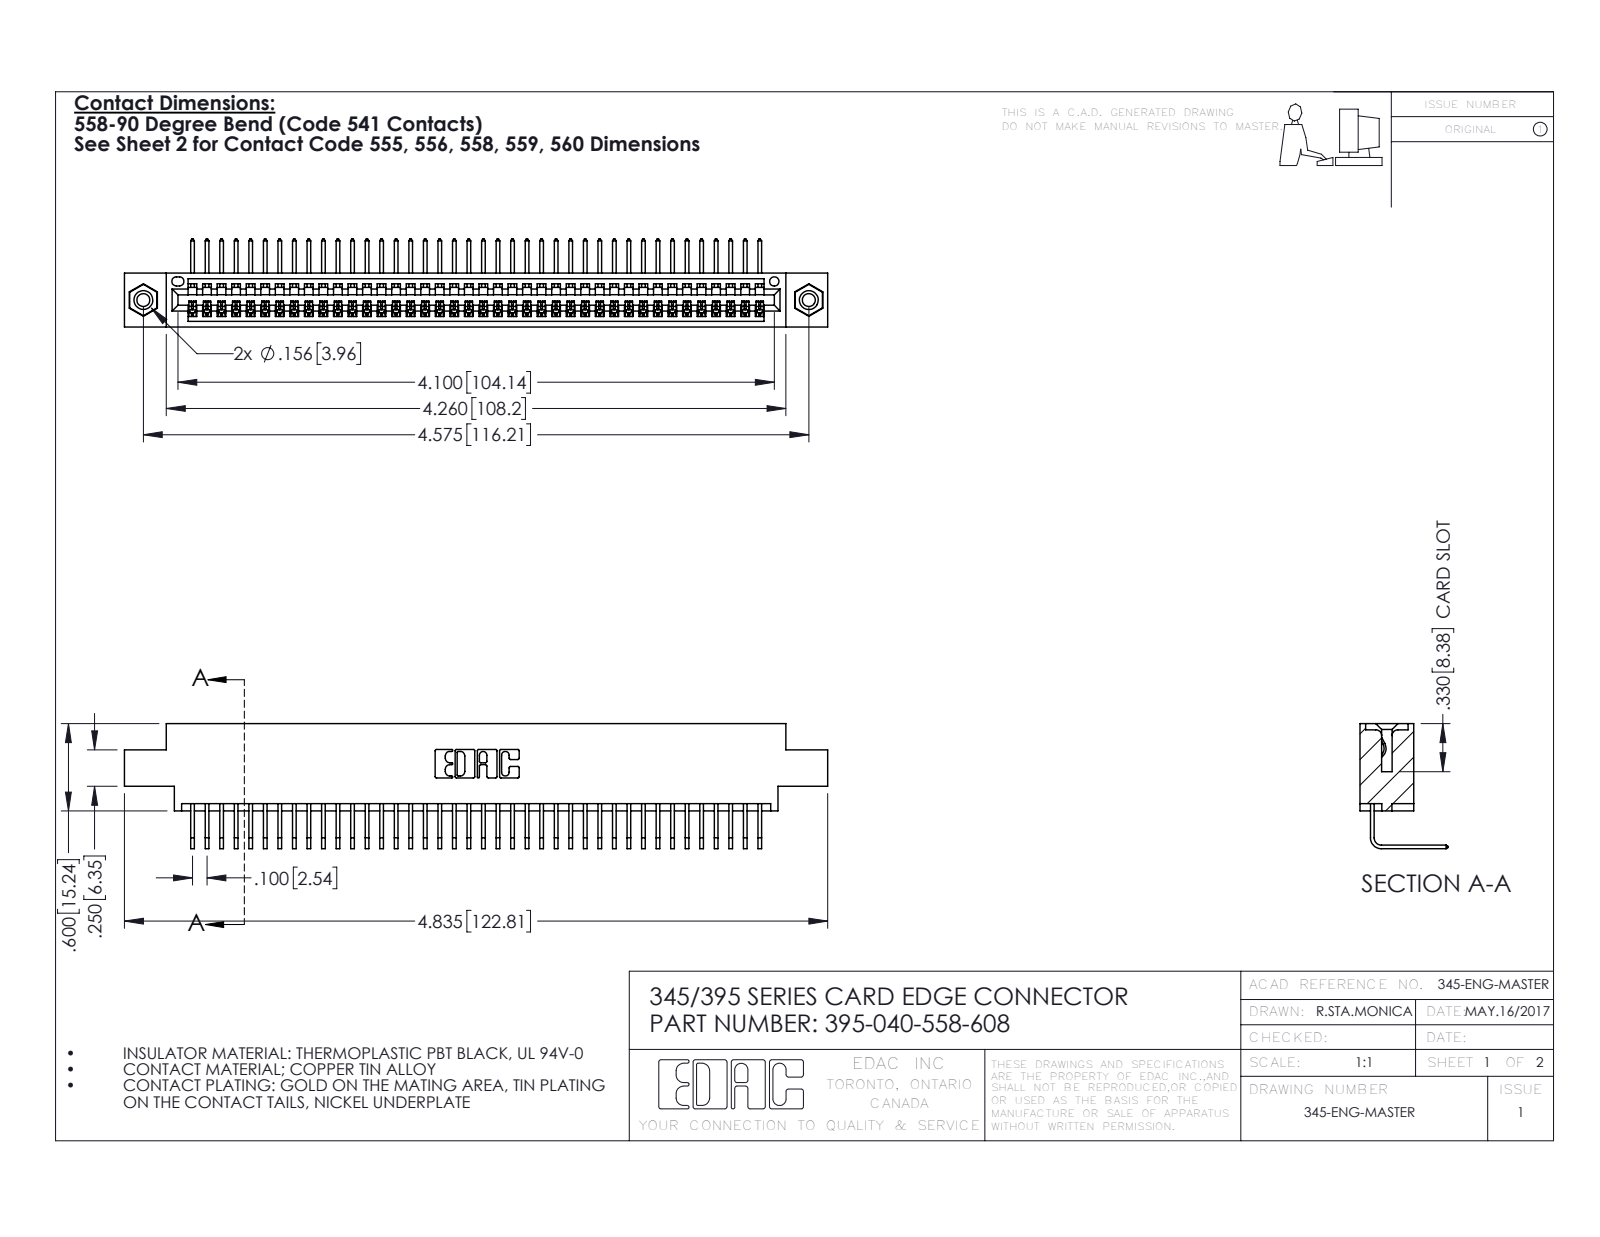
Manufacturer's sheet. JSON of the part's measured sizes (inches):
{"part_name": "395-040-558-608; 345-292-001_558 Tail - 2; 345-250-001_345-250-003-102; 345 Part_0.170 Offset - 0.156 Dia-TI", "step_written_by": "SolidWorks 2016 (CONFIG_CONTROL_DESIGN)", "units": "inches", "bodies": {"solids": 43, "faces": 2590, "planar": 1796, "cylindrical": 778, "other": 16}, "overall_size": [4.835, 0.859, 0.605], "volume_in3": 0.712, "surface_area_in2": 25.42, "round_holes": [[0.089, 2], [0.125, 2], [0.156, 2], [0.064, 1]], "round_bosses_or_shafts": [[0.155, 2]], "partial_cylinders_radius": [[0.006, 80], [0.01, 22], [0.007, 6], [0.031, 6], [0.026, 3], [0.031, 2], [0.04, 2], [0.014, 1]], "face_to_face_distances": [0.072, 0.298, 0.37, 0.2, 0.098, 0.272, 0.025, 0.225, 0.175, 0.149], "hole_center_spacings": [0.27, 4.339, 4.575]}
